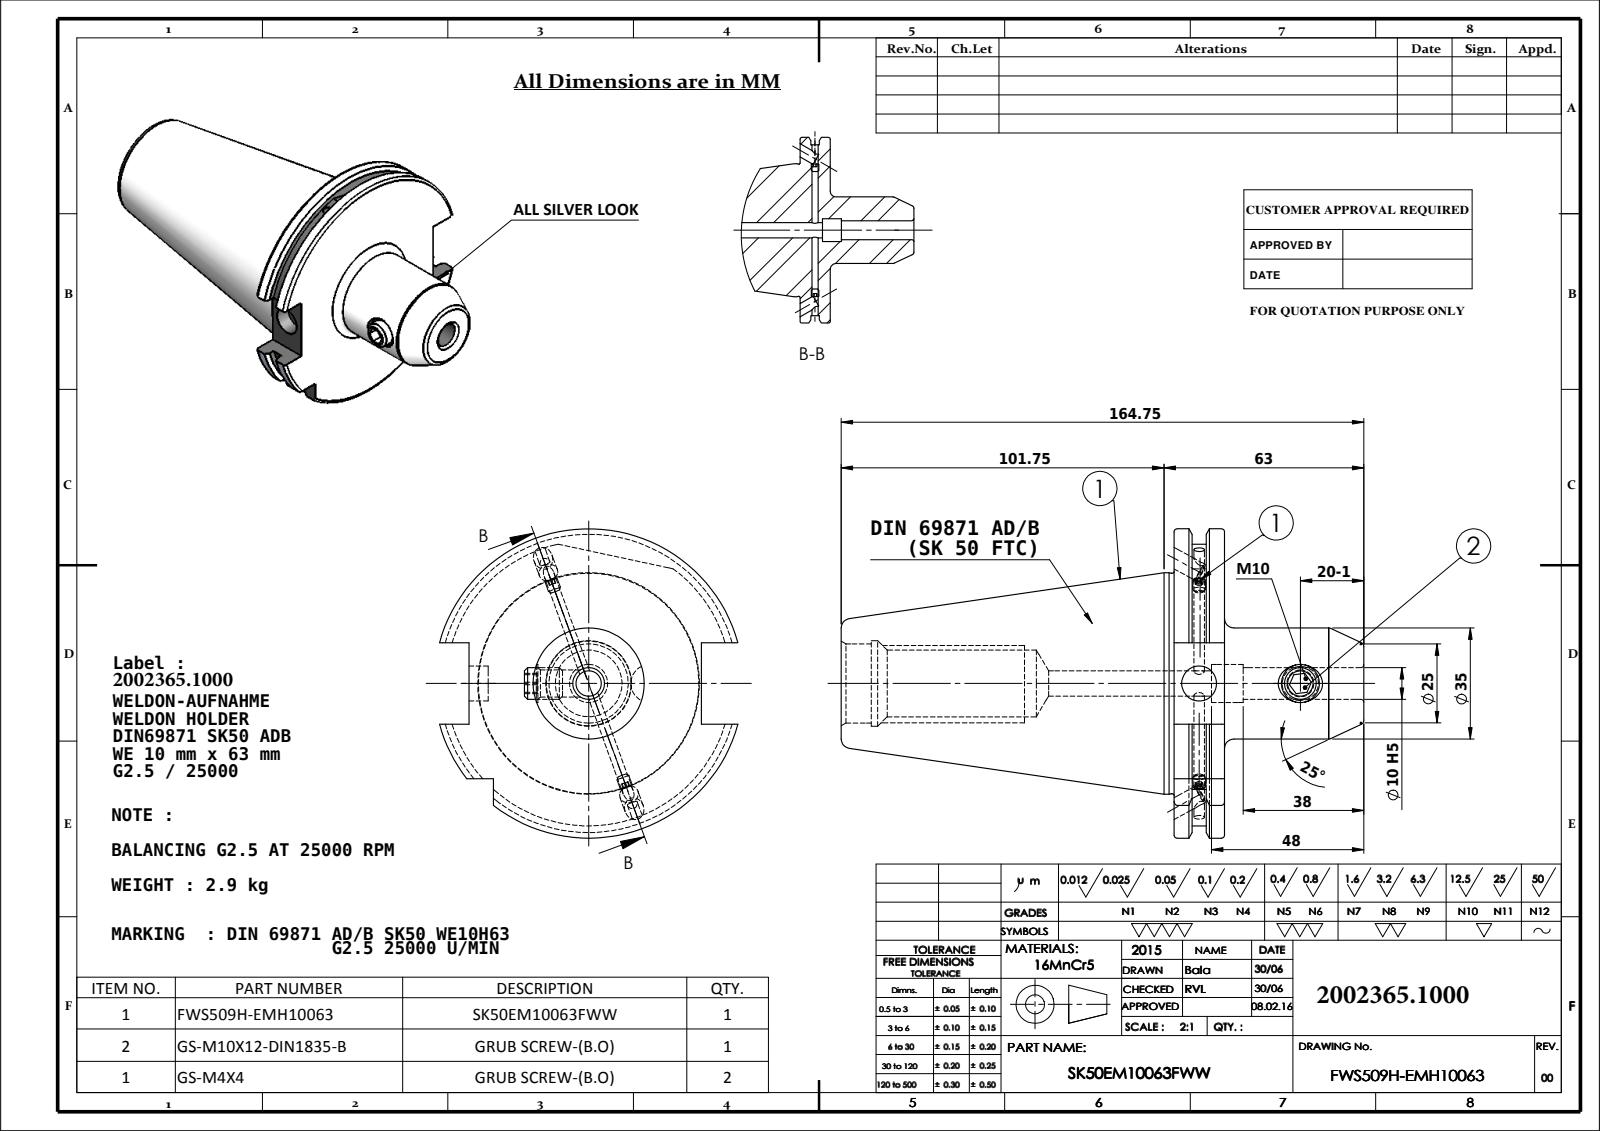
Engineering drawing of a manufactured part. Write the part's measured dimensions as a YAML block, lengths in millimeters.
part_name: "91506-WE710063; SK50EM10063FWW R01; M10X12; Copy of M4X4_DIN 913 - M4 x 4-N"
step_written_by: "SolidWorks 2009 (CONFIG_CONTROL_DESIGN)"
units: millimeters
bodies: {solids: 4, faces: 168, planar: 53, cylindrical: 55, other: 60}
overall_size: [164.75, 97.5, 94.05]
volume: 370365
surface_area: 49731
round_holes:
  - {diameter: 6, count: 2}
  - {diameter: 12, count: 2}
  - {diameter: 3.3, count: 1}
  - {diameter: 8, count: 1}
  - {diameter: 8.5, count: 1}
  - {diameter: 10, count: 1}
  - {diameter: 11, count: 1}
  - {diameter: 21, count: 1}
  - {diameter: 25, count: 1}
  - {diameter: 27, count: 1}
round_bosses_or_shafts:
  - {diameter: 4, count: 2}
  - {diameter: 69.85, count: 1}
  - {diameter: 69.45, count: 1}
  - {diameter: 35, count: 1}
  - {diameter: 10, count: 1}
partial_cylinders:
  - {radius: 44.9, count: 1}
  - {radius: 48.75, count: 1}
face_to_face_distances: [15.9, 5.66, 10.24, 10.15, 4.49, 5.75, 104.95, 110.61, 115.1, 120.85]
hole_center_spacings: [31.9]
